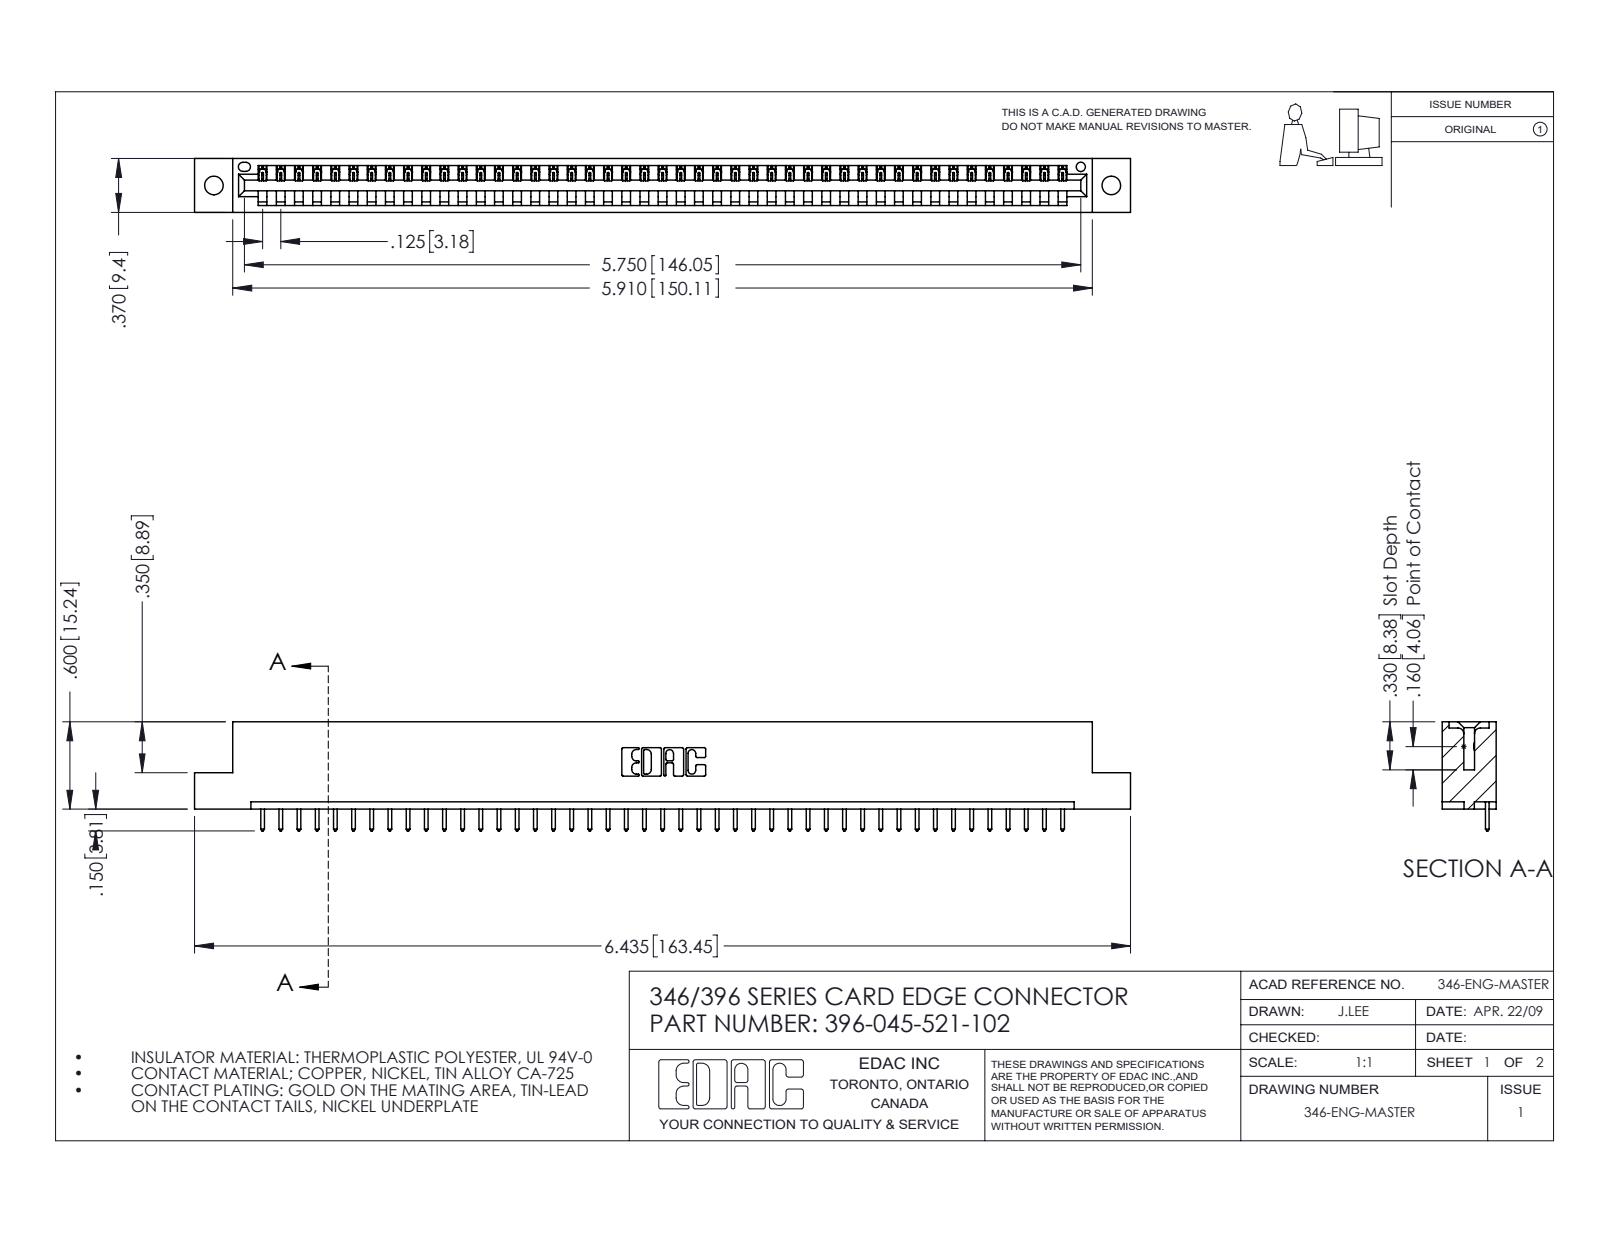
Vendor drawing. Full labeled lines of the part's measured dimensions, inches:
Part name (STEP PRODUCT): 396-045-521-102; 346 Part_Flush Mounting Lugs - 0.128 Dia; 345-292-001_345-293-121
STEP written by: SolidWorks 2016 (CONFIG_CONTROL_DESIGN)
Units: inches
Bodies: 46 solids, 2732 faces (1876 planar, 856 cylindrical, 0 other)
Overall size (bounding box): 6.435 × 0.75 × 0.37
Volume: 0.946 in³ · Surface area: 28.87 in²
Round holes (diameter × count): ⌀0.128 ×2, ⌀0.064 ×1
Partial cylindrical surfaces — rounded edges, fillets, slot ends (radius × count): R0.006 ×90, R0.01 ×90, R0.01 ×22, R0.007 ×6, R0.031 ×6, R0.026 ×3, R0.031 ×2, R0.04 ×2
Main face-to-face distances: 0.048, 0.322, 0.37, 0.25, 0.072, 0.298, 0.025, 0.148, 0.222, 0.1
Hole centre spacings: 0.246, 5.961, 6.17
